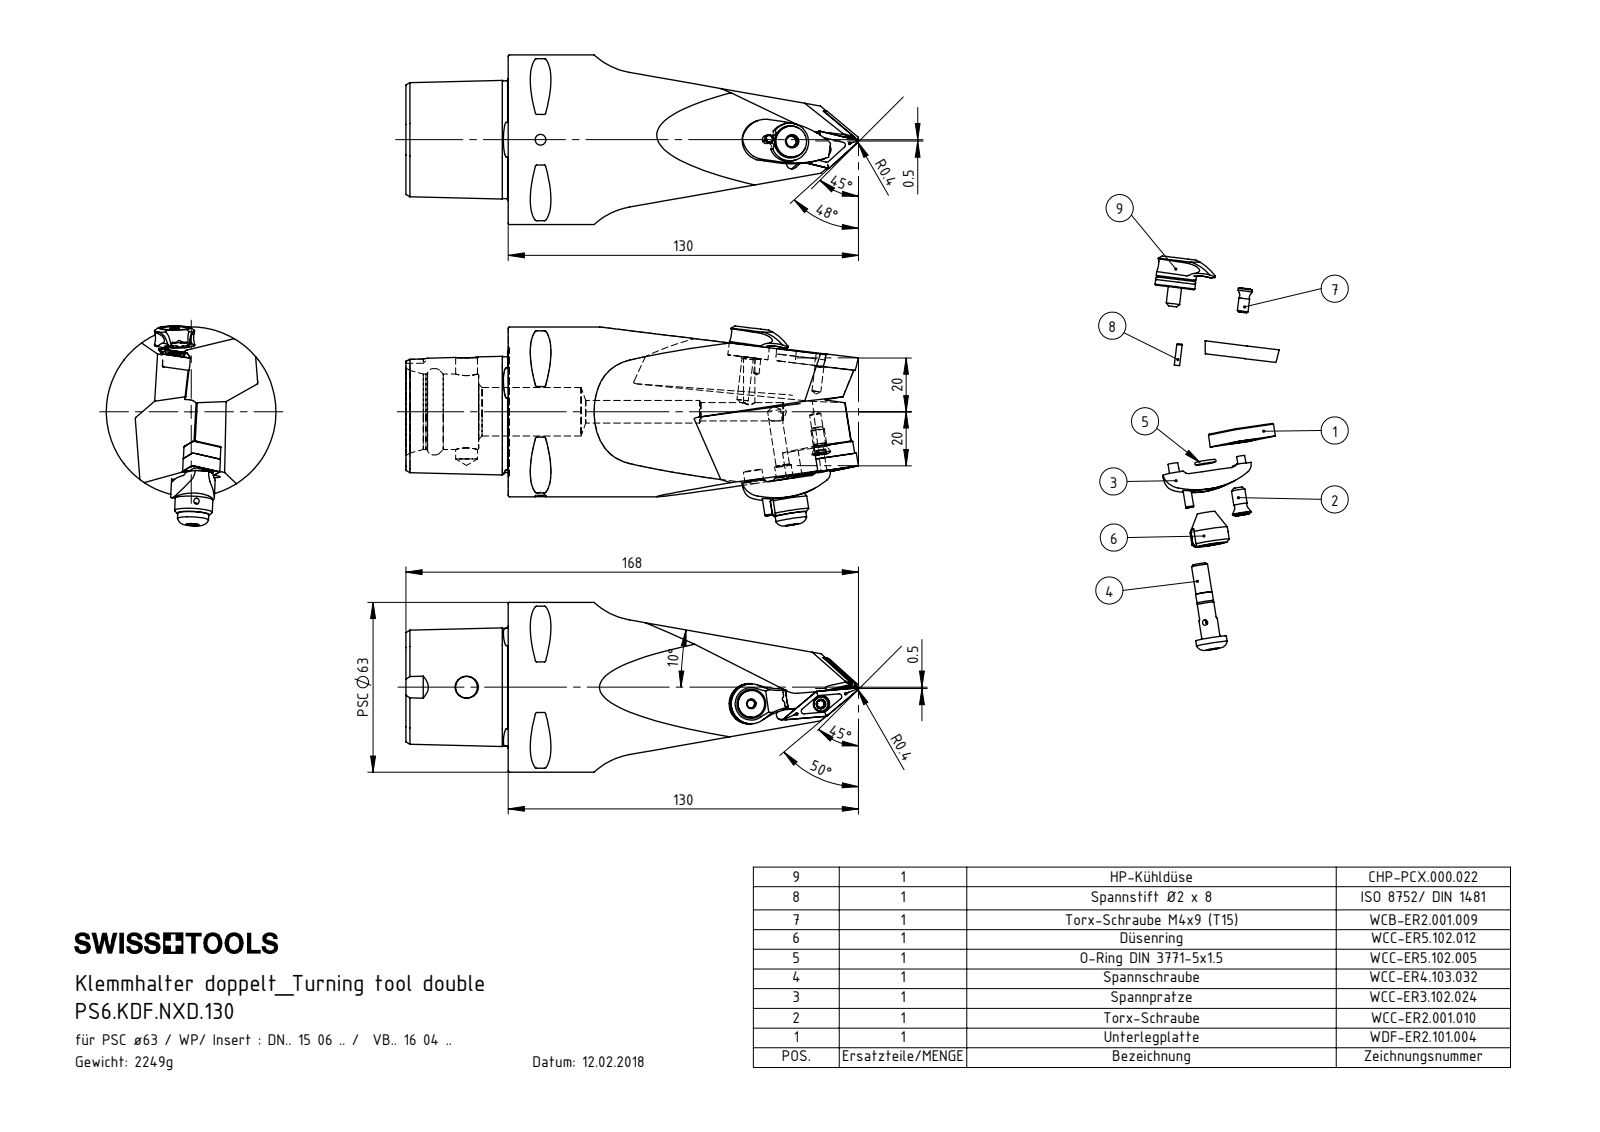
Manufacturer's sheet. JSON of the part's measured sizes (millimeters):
{"part_name": "DNMG150404; WCC-ER3.102.024_C; CHP-PCX.000.022_B; PS6-KDF.NXD.130_A (+8 more)", "step_written_by": "SolidWorks 2017 (AUTOMOTIVE_DESIGN)", "units": "millimeters", "bodies": {"solids": 15, "faces": 666, "planar": 162, "cylindrical": 198, "other": 306}, "overall_size": [168.01, 74.24, 63], "volume_mm3": 285607, "surface_area_mm2": 47380, "round_holes": [[2, 4], [4.2, 3], [7, 2], [1.2, 1], [2.4, 1], [3, 1], [3.3, 1], [4, 1], [4.4, 1], [5, 1], [5.16, 1], [5.3, 1]], "round_bosses_or_shafts": [[5, 2], [3, 2], [63, 1], [14.85, 1], [14, 1], [13.4, 1], [11.5, 1], [10, 1]], "partial_cylinders_radius": [[0.5, 14], [1, 7], [0.39, 6], [0.69, 6], [6, 5], [0.4, 4], [1.2, 3], [1.5, 3]], "face_to_face_distances": [38, 4.76, 25.67, 21.23, 4.44, 24.88, 16.47, 9.2, 12.11, 27], "hole_center_spacings": [4.5, 7.96, 8.01, 8.2, 14.79, 22.99, 23, 23.04]}
